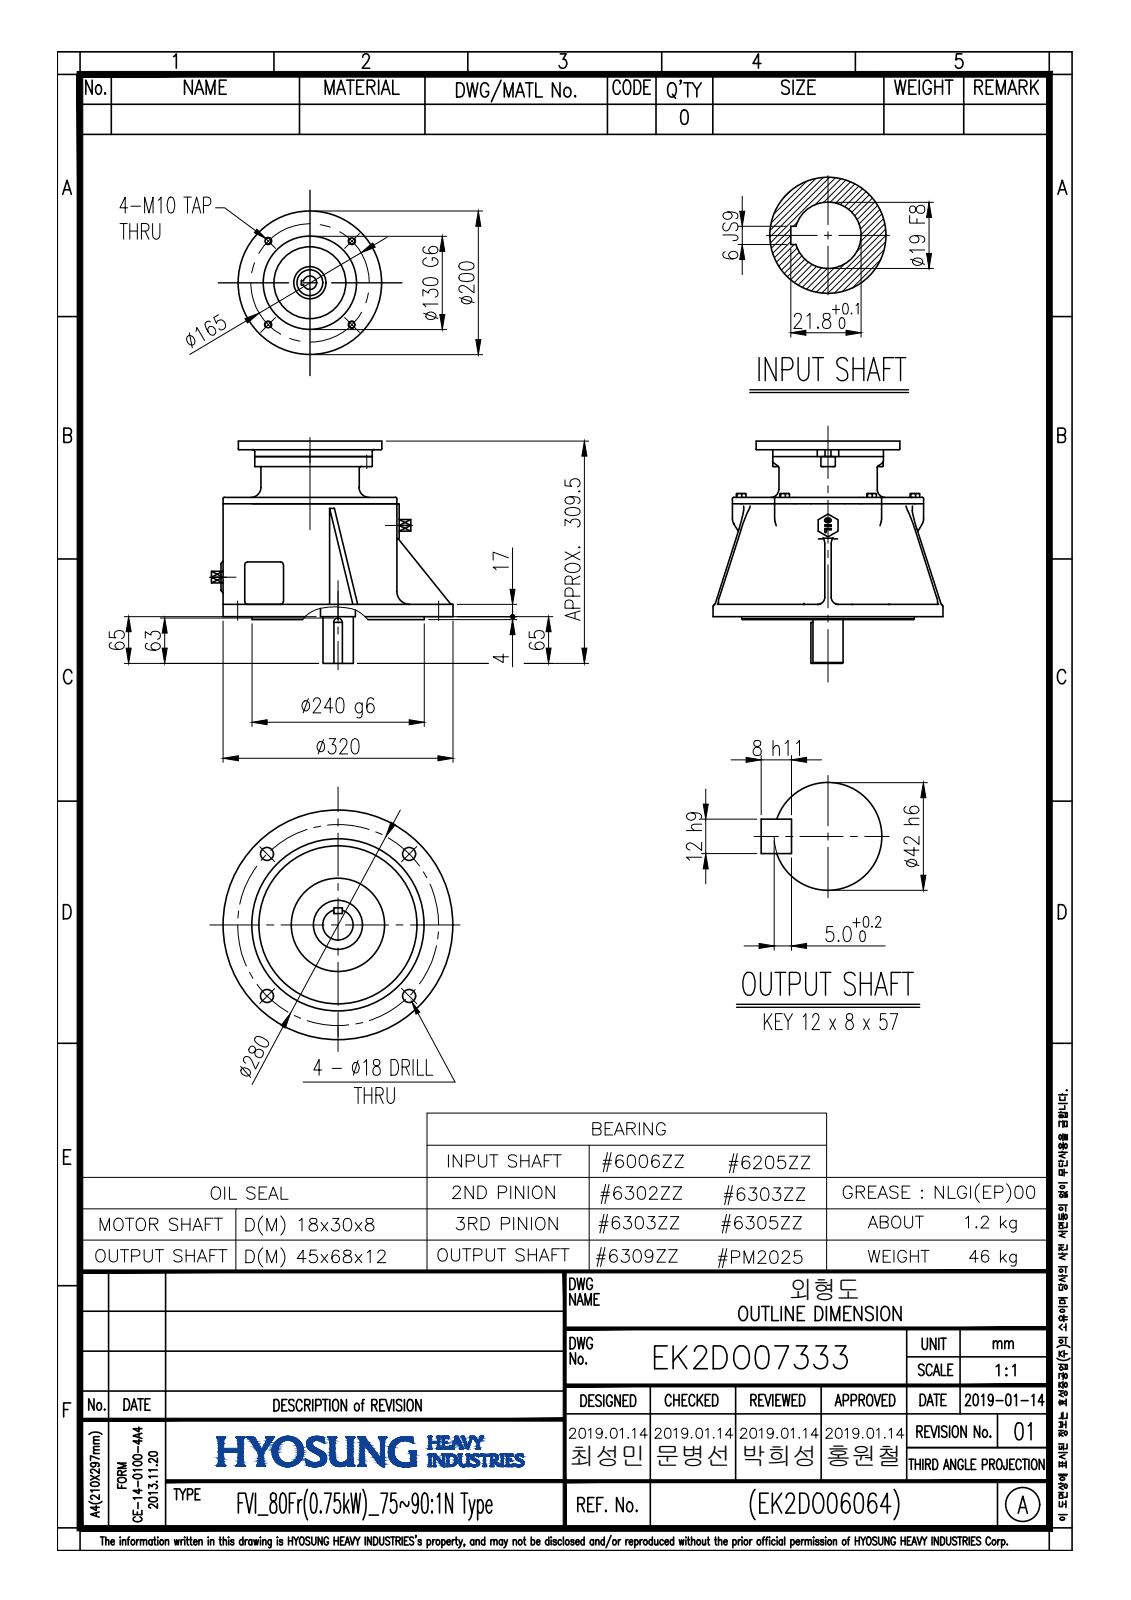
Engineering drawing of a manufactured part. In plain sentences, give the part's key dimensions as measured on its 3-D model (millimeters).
The part is named "FN_FVI_0.4_R75". Its 3-D file was written by "SolidWorks 2021 (AUTOMOTIVE_DESIGN)". It is 10 solids with 691 faces: 172 planar, 206 cylindrical and 313 other. Overall it measures 323.05 by 320 by 309.5 millimeters. Its volume is 10 420 000 cubic millimeters and its surface area 601 404 square millimeters. Round holes: 6 of diameter 8.5, 6 of diameter 9, 4 of diameter 6.65, 4 of diameter 18, 3 of diameter 6.8, 3 of diameter 9.5, 2 of diameter 6, 2 of diameter 6.65, 1 of diameter 1.5, 1 of diameter 14.95, 1 of diameter 50, 1 of diameter 64. Round bosses or shafts: 6 of diameter 11.6, 6 of diameter 8, 1 of diameter 320, 1 of diameter 242, 1 of diameter 240, 1 of diameter 227, 1 of diameter 222, 1 of diameter 200. Partial cylindrical surfaces (rounded edges, fillets, slot ends): 27 of radius 3, 26 of radius 1, 16 of radius 16, 10 of radius 10, 6 of radius 2, 6 of radius 21, 3 of radius 13, 3 of radius 133. The main face-to-face distances are 157, 223, 66, 9, 17, 57, 166, 206, 149, 140. The hole center spacings are 121, 144.51, 193.49, 209.58, 46.5, 65.77, 66.38, 82.51.
